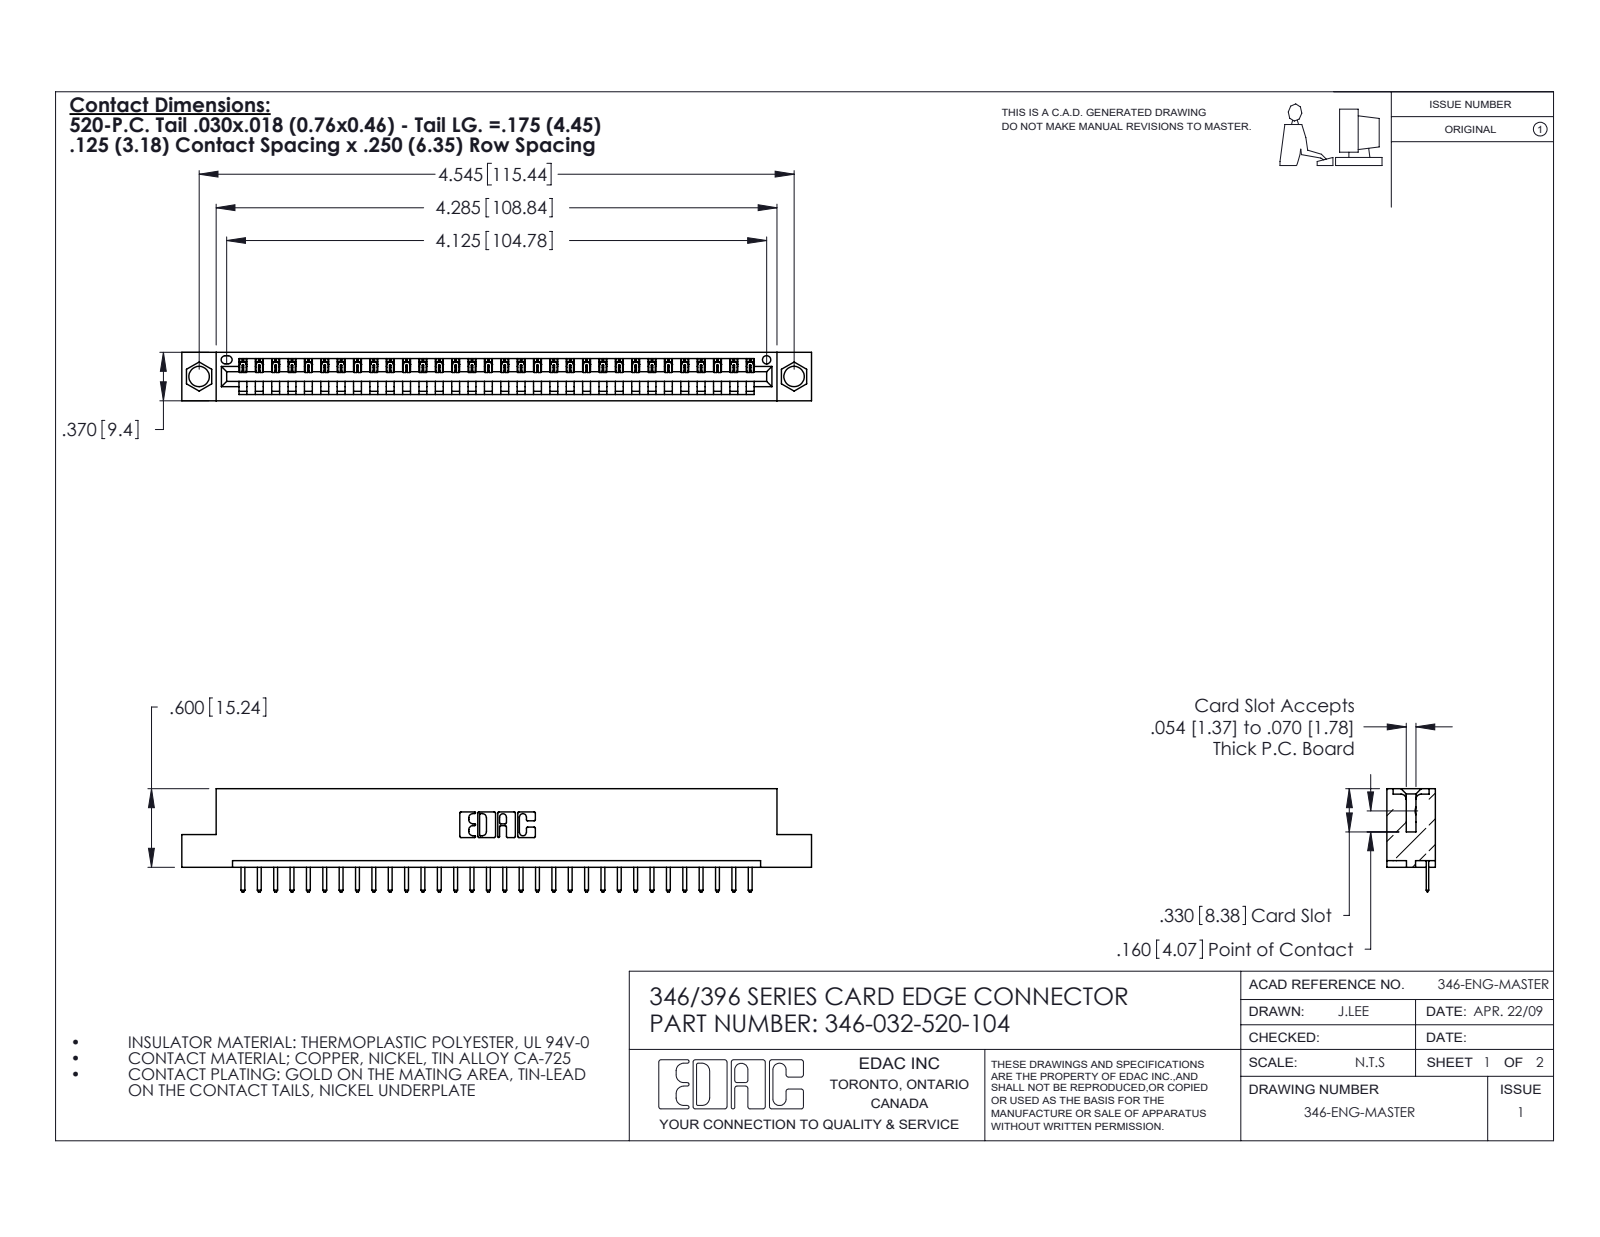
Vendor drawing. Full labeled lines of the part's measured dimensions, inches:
Part name (STEP PRODUCT): 346-032-520-104; 345-292-001_345-293-120; 346 Part_Flush Mounting Lugs - 0.156 Dia-TH
STEP written by: SolidWorks 2020 (CONFIG_CONTROL_DESIGN)
Units: inches
Bodies: 33 solids, 2120 faces (1434 planar, 686 cylindrical, 0 other)
Overall size (bounding box): 4.81 × 0.788 × 0.37
Volume: 0.697 in³ · Surface area: 21.24 in²
Round holes (diameter × count): ⌀0.156 ×2, ⌀0.064 ×1
Partial cylindrical surfaces — rounded edges, fillets, slot ends (radius × count): R0.01 ×66, R0.006 ×64, R0.01 ×22, R0.007 ×6, R0.031 ×6, R0.026 ×3, R0.031 ×2, R0.04 ×2
Main face-to-face distances: 0.048, 0.322, 0.37, 0.25, 0.148, 0.222, 0.1, 0.174, 0.072, 0.298
Hole centre spacings: 0.246, 4.337, 4.545
